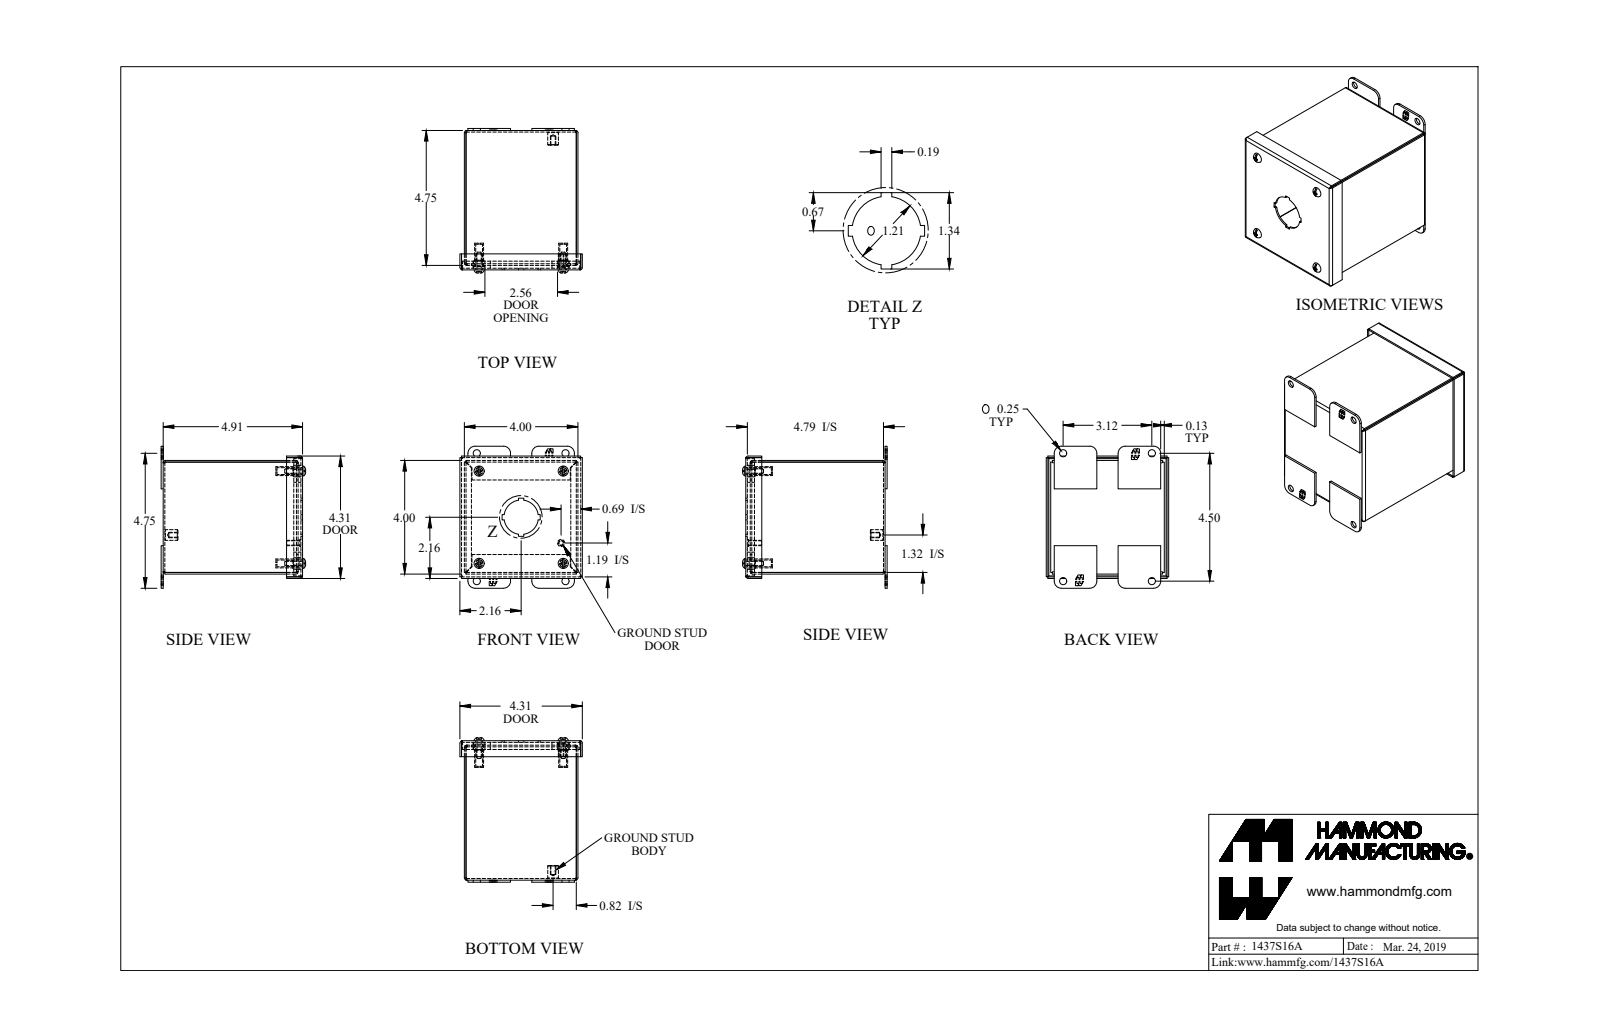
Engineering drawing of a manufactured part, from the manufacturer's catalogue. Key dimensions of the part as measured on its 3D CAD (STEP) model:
Part name (STEP PRODUCT): 1437S16A_Default
STEP written by: SolidWorks 2019 (CONFIG_CONTROL_DESIGN)
Units: inches
Bodies: 21 solids, 541 faces (371 planar, 140 cylindrical, 30 other)
Overall size (bounding box): 5.089 × 5 × 4.312
Volume: 9.233 in³ · Surface area: 294.7 in²
Round holes (diameter × count): ⌀0.25 ×8, ⌀0.065 ×4, ⌀0.239 ×4, ⌀0.253 ×4, ⌀0.406 ×4, ⌀0.156 ×1, ⌀1.21 ×1
Round bosses / shafts (diameter × count): ⌀0.19 ×5, ⌀0.406 ×4, ⌀0.315 ×4, ⌀0.148 ×4, ⌀0.375 ×1, ⌀0.25 ×1
Partial cylindrical surfaces — rounded edges, fillets, slot ends (radius × count): R0.029 ×12, R0.086 ×12, R0.25 ×8, R0.171 ×4, R0.125 ×2
Main face-to-face distances: 0.057, 3.943, 4.85, 4, 3.886, 4.907, 0.156, 4.099, 4.793, 0.157
Hole centre spacings: 3.25, 0.63, 2.961, 3.107, 3.876, 4.396, 4.927, 2.962
